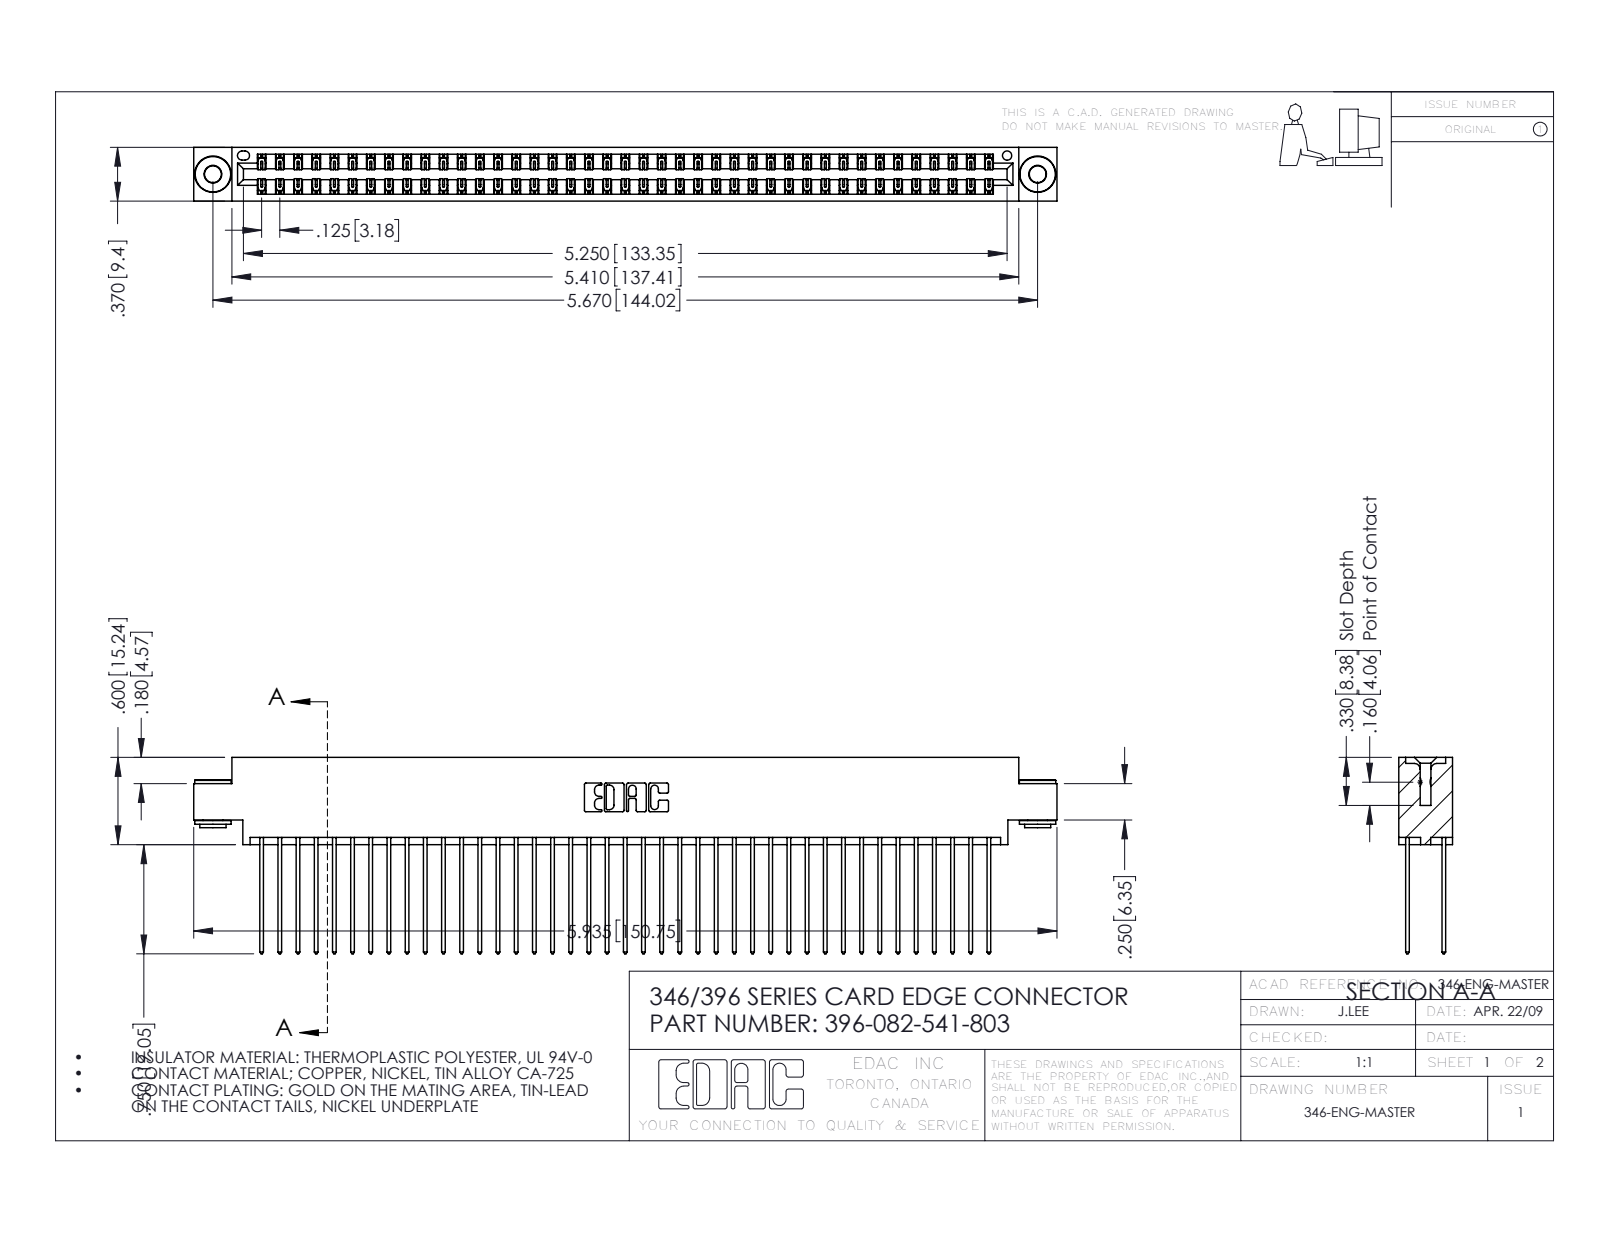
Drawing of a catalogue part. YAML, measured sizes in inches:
part_name: "346 Part_0.170 Offset - 0.156 Dia-TH; 345-250-002_345-250-002-102; 396-082-541-803; 345-292-001_345-293-141"
step_written_by: "SolidWorks 2016 (CONFIG_CONTROL_DESIGN)"
units: inches
bodies: {solids: 85, faces: 4428, planar: 2960, cylindrical: 1460, other: 8}
overall_size: [5.935, 1.35, 0.37]
volume: 0.917
surface_area: 36.1
round_holes:
  - {diameter: 0.116, count: 2}
  - {diameter: 0.156, count: 2}
  - {diameter: 0.064, count: 1}
round_bosses_or_shafts:
  - {diameter: 0.25, count: 2}
  - {diameter: 0.18, count: 2}
  - {diameter: 0.136, count: 2}
partial_cylinders:
  - {radius: 0.006, count: 123}
  - {radius: 0.01, count: 82}
  - {radius: 0.01, count: 22}
  - {radius: 0.007, count: 6}
  - {radius: 0.031, count: 6}
  - {radius: 0.026, count: 3}
  - {radius: 0.014, count: 2}
  - {radius: 0.022, count: 2}
face_to_face_distances: [0.048, 0.322, 0.25, 0.025, 0.072, 0.298, 0.37, 0.275, 0.225, 0.148]
hole_center_spacings: [0.246, 5.461, 5.67]
